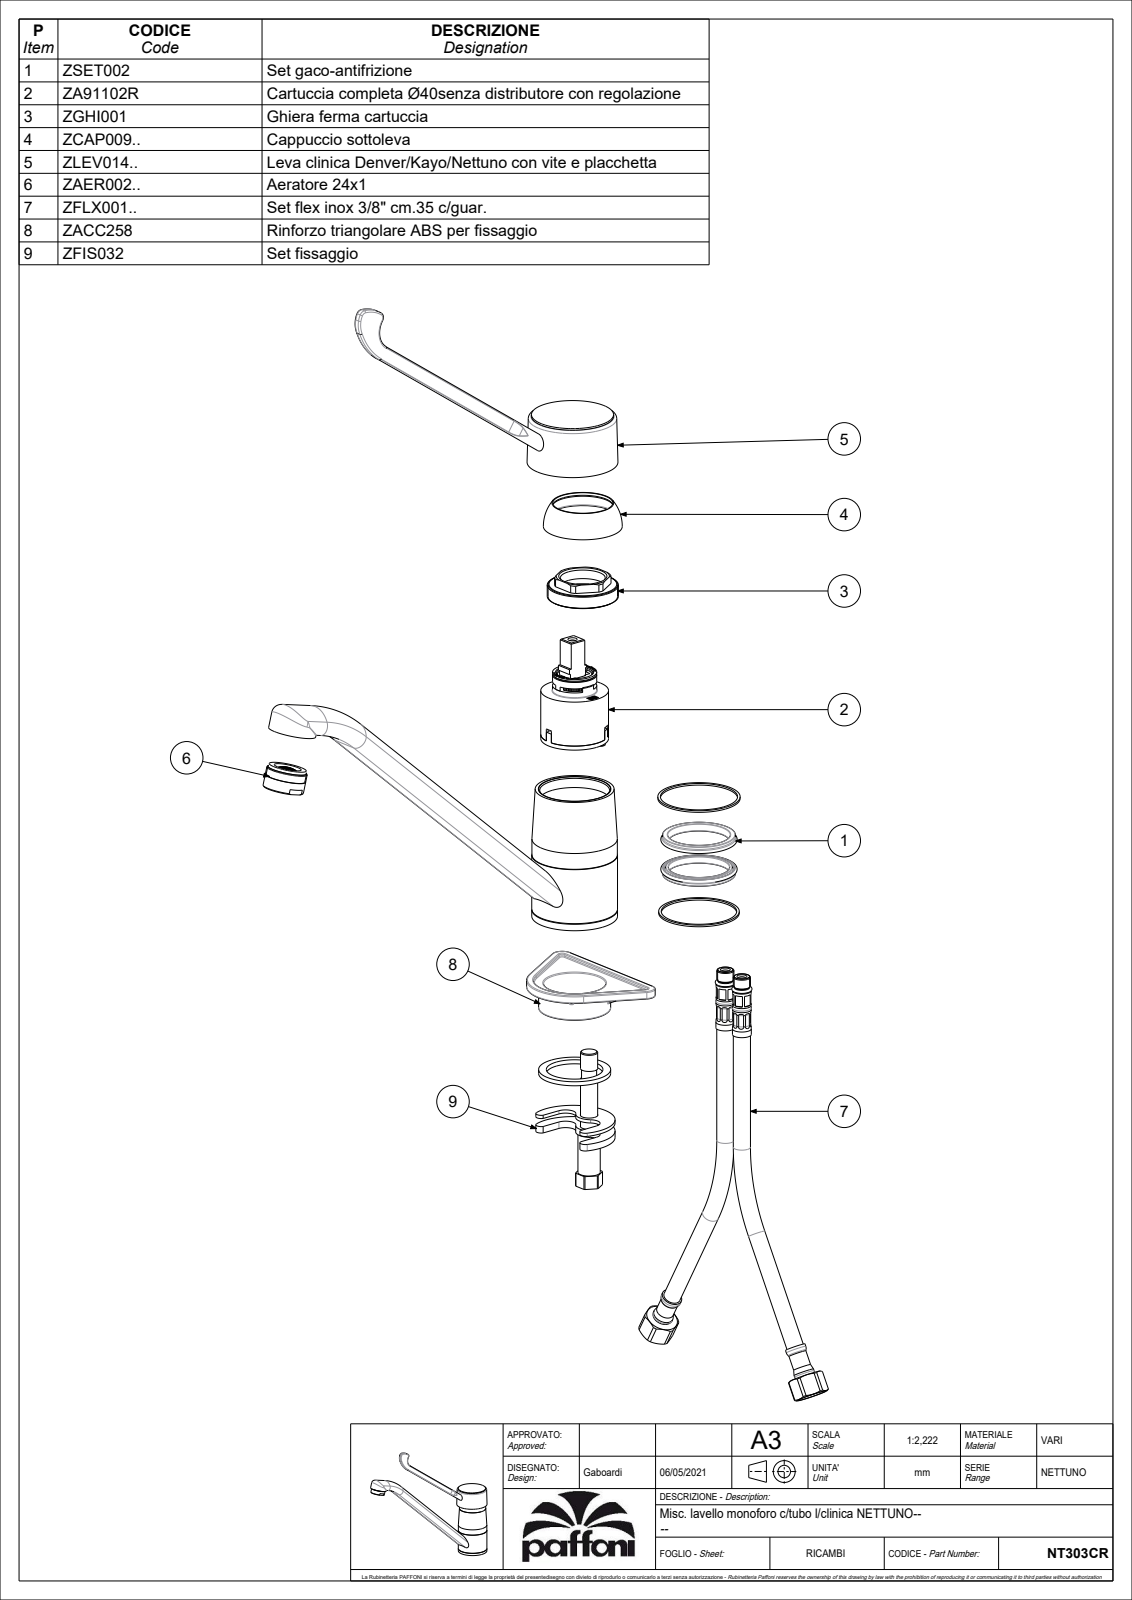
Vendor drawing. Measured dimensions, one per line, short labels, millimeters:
name: NT303CR
written by: CREO PARAMETRIC BY PTC INC, 2020044 (CONFIG_CONTROL_DESIGN)
unit: mm
bodies: 4 solids, 2640 faces (2053 planar, 360 cylindrical, 227 other)
size: 253.52 × 218.78 × 53
volume: 152 880 mm³; area: 119 019 mm²
holes: 5× ⌀9, 3× ⌀11, 2× ⌀7, 2× ⌀8, 2× ⌀11.7, 2× ⌀21, 1× ⌀3, 1× ⌀3.3, 1× ⌀4, 1× ⌀4.3, 1× ⌀5, 1× ⌀9.25
bosses: 1× ⌀50, 1× ⌀49.8, 1× ⌀47.85, 1× ⌀46.5, 1× ⌀44.8, 1× ⌀43.7, 1× ⌀40.5, 1× ⌀40
rounds: 40× R0.5, 24× R0.2, 4× R0.3, 4× R4.25, 4× R5.5, 2× R12, 2× R15.25, 2× R16.5
face distances: 1.25, 4.5, 7.5, 0.5, 2.5, 1.5, 5, 49.5, 17, 1
hole spacings: 0.54, 1.12, 1.51, 2, 2.52, 3.04, 8.5, 8.6
